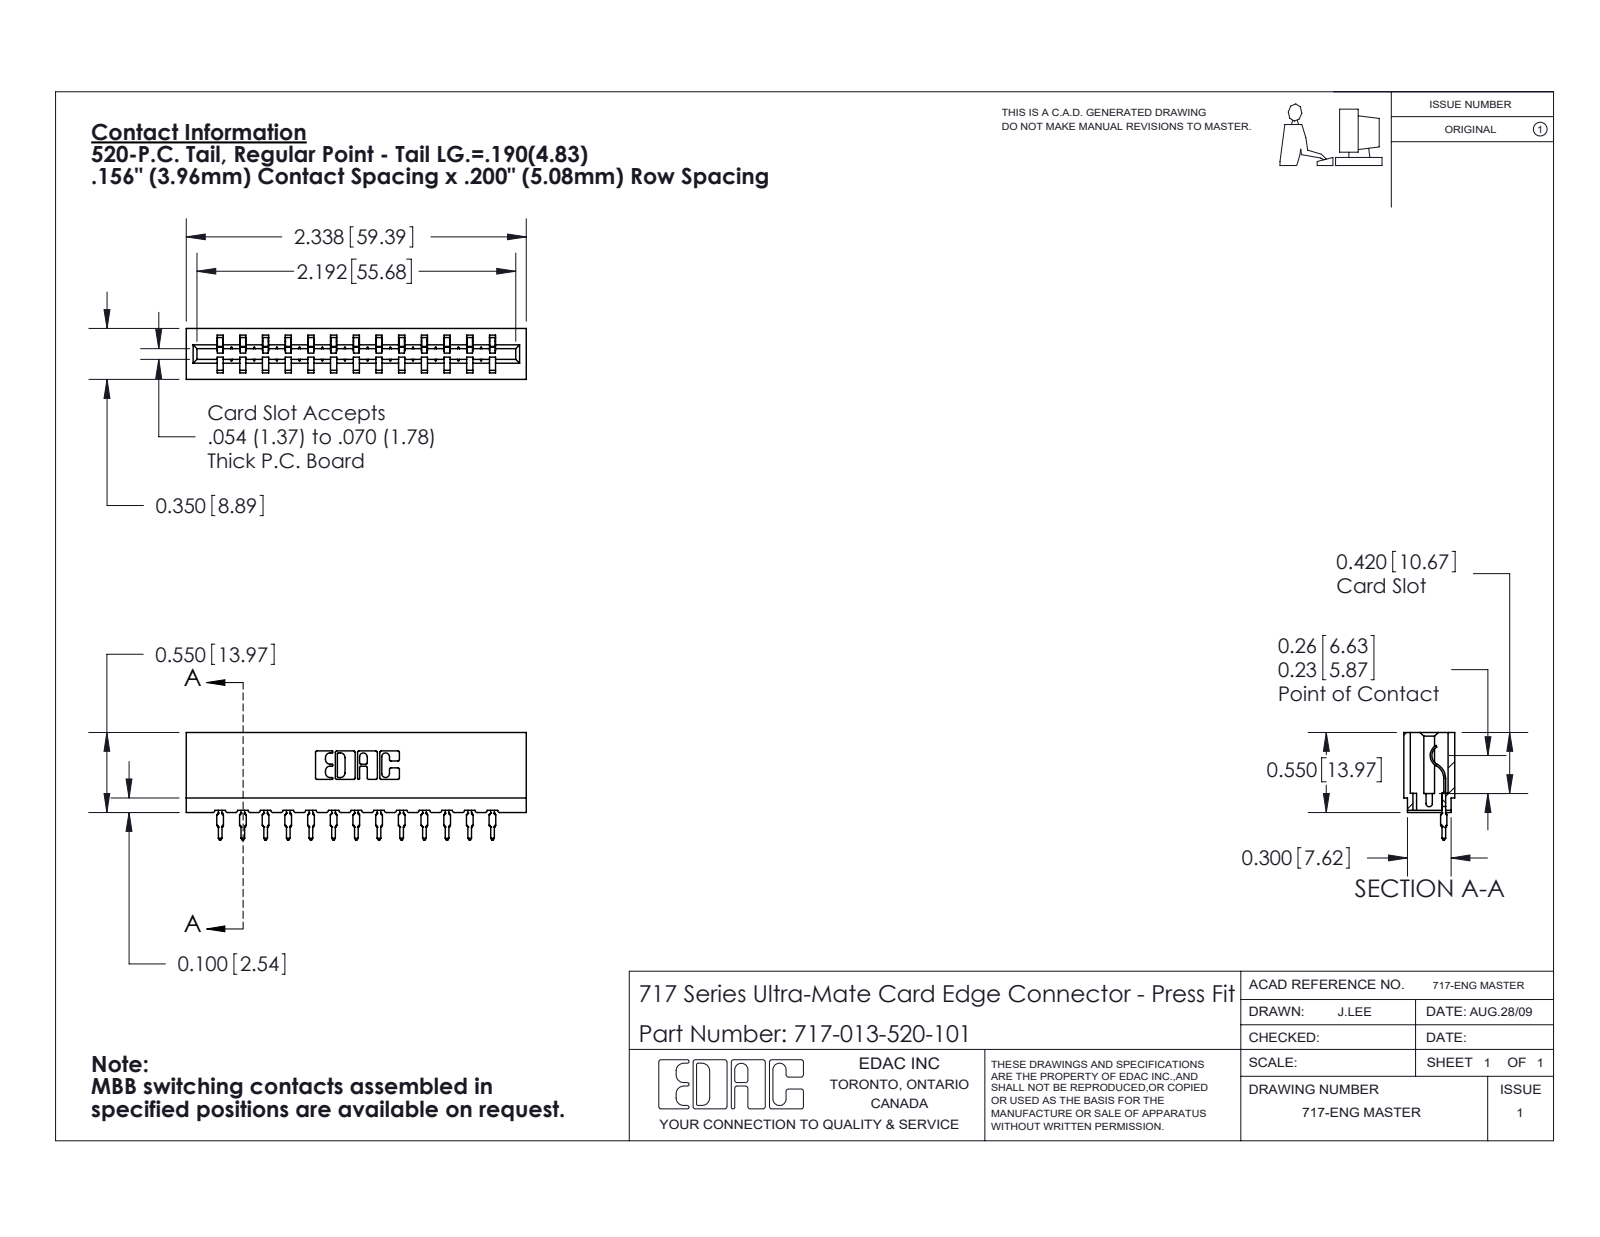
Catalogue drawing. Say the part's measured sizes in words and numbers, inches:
The part is named "717-013-520-101; 717 Part_Insulator Option - 06; 745-292-001_520". Its 3-D file was written by "SolidWorks 2020 (CONFIG_CONTROL_DESIGN)". It is 14 solids with 1563 faces: 938 planar, 287 cylindrical and 338 other. Overall it measures 2.338 by 0.739 by 0.35 inches. Its volume is 0.313 cubic inches and its surface area 10.53 square inches. Partial cylindrical surfaces (rounded edges, fillets, slot ends): 26 of radius 0.015, 26 of radius 0.021, 22 of radius 0.01, 6 of radius 0.007, 6 of radius 0.031, 4 of radius 0.005, 4 of radius 0.011, 3 of radius 0.026. The main face-to-face distances are 0.212, 0.138, 0.156, 0.35, 0.624, 0.468, 0.312, 0.198, 0.074, 0.042.
